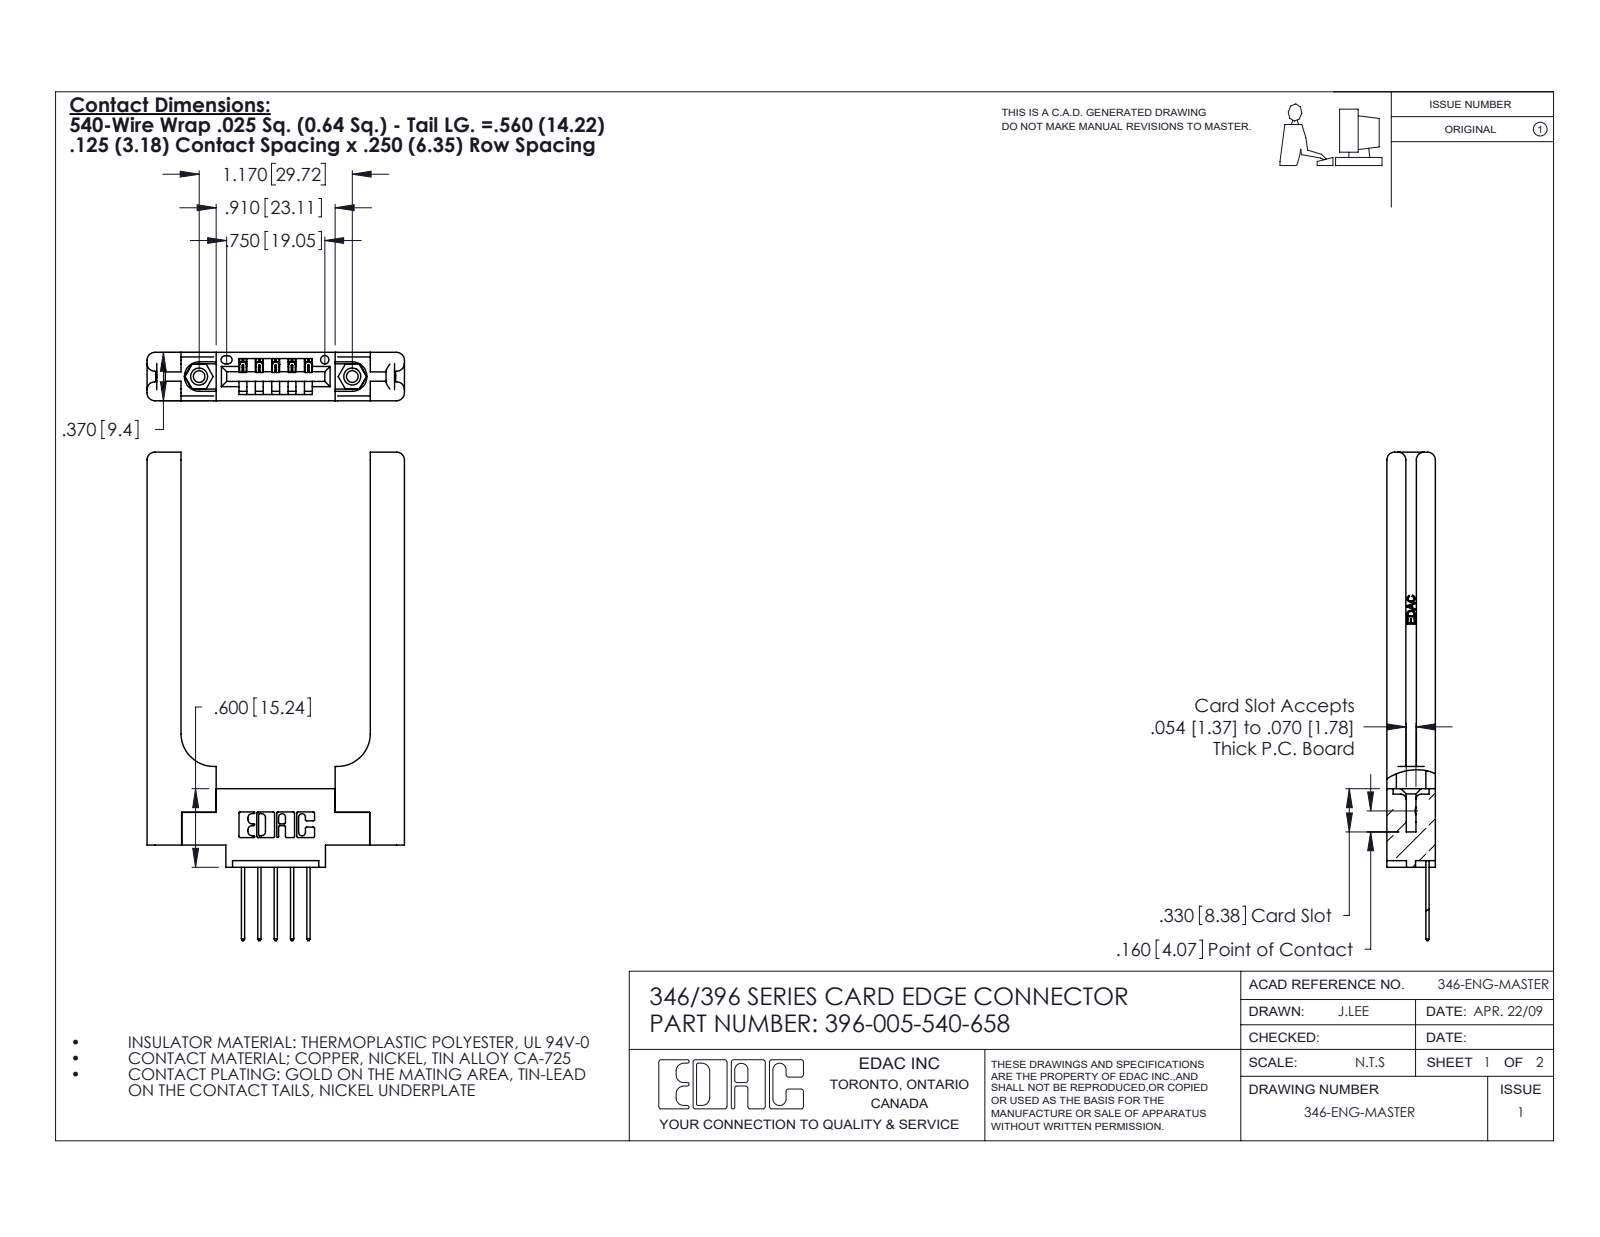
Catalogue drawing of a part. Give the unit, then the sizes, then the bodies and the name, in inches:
Units: inches
Overall size (bounding box): 3.73 × 1.966 × 0.37
Round holes (diameter × count): ⌀0.089 ×2, ⌀0.125 ×2, ⌀0.156 ×2, ⌀0.064 ×1
Round bosses / shafts (diameter × count): ⌀0.155 ×2
Partial cylindrical surfaces — rounded edges, fillets, slot ends (radius × count): R0.01 ×22, R0.06 ×16, R0.006 ×10, R0.01 ×10, R0.007 ×6, R0.031 ×6, R0.026 ×3, R0.03 ×2
Main face-to-face distances: 0.37, 0.15, 0.22, 0.072, 1.446, 0.148, 0.25, 0.075, 0.071, 0.26
Hole centre spacings: 0.246, 0.969, 1.17
Volume: 0.725 in³ · Surface area: 16.21 in²
Bodies: 10 solids, 686 faces (442 planar, 184 cylindrical, 60 other)
Part name (STEP PRODUCT): 396-005-540-658; 346 Part_0.170 Offset - 0.156 Dia-TH; 345-250-001_345-250-001-102; 345-292-001_345-293-140 (+1 more)
STEP written by: SolidWorks 2020 (CONFIG_CONTROL_DESIGN)
